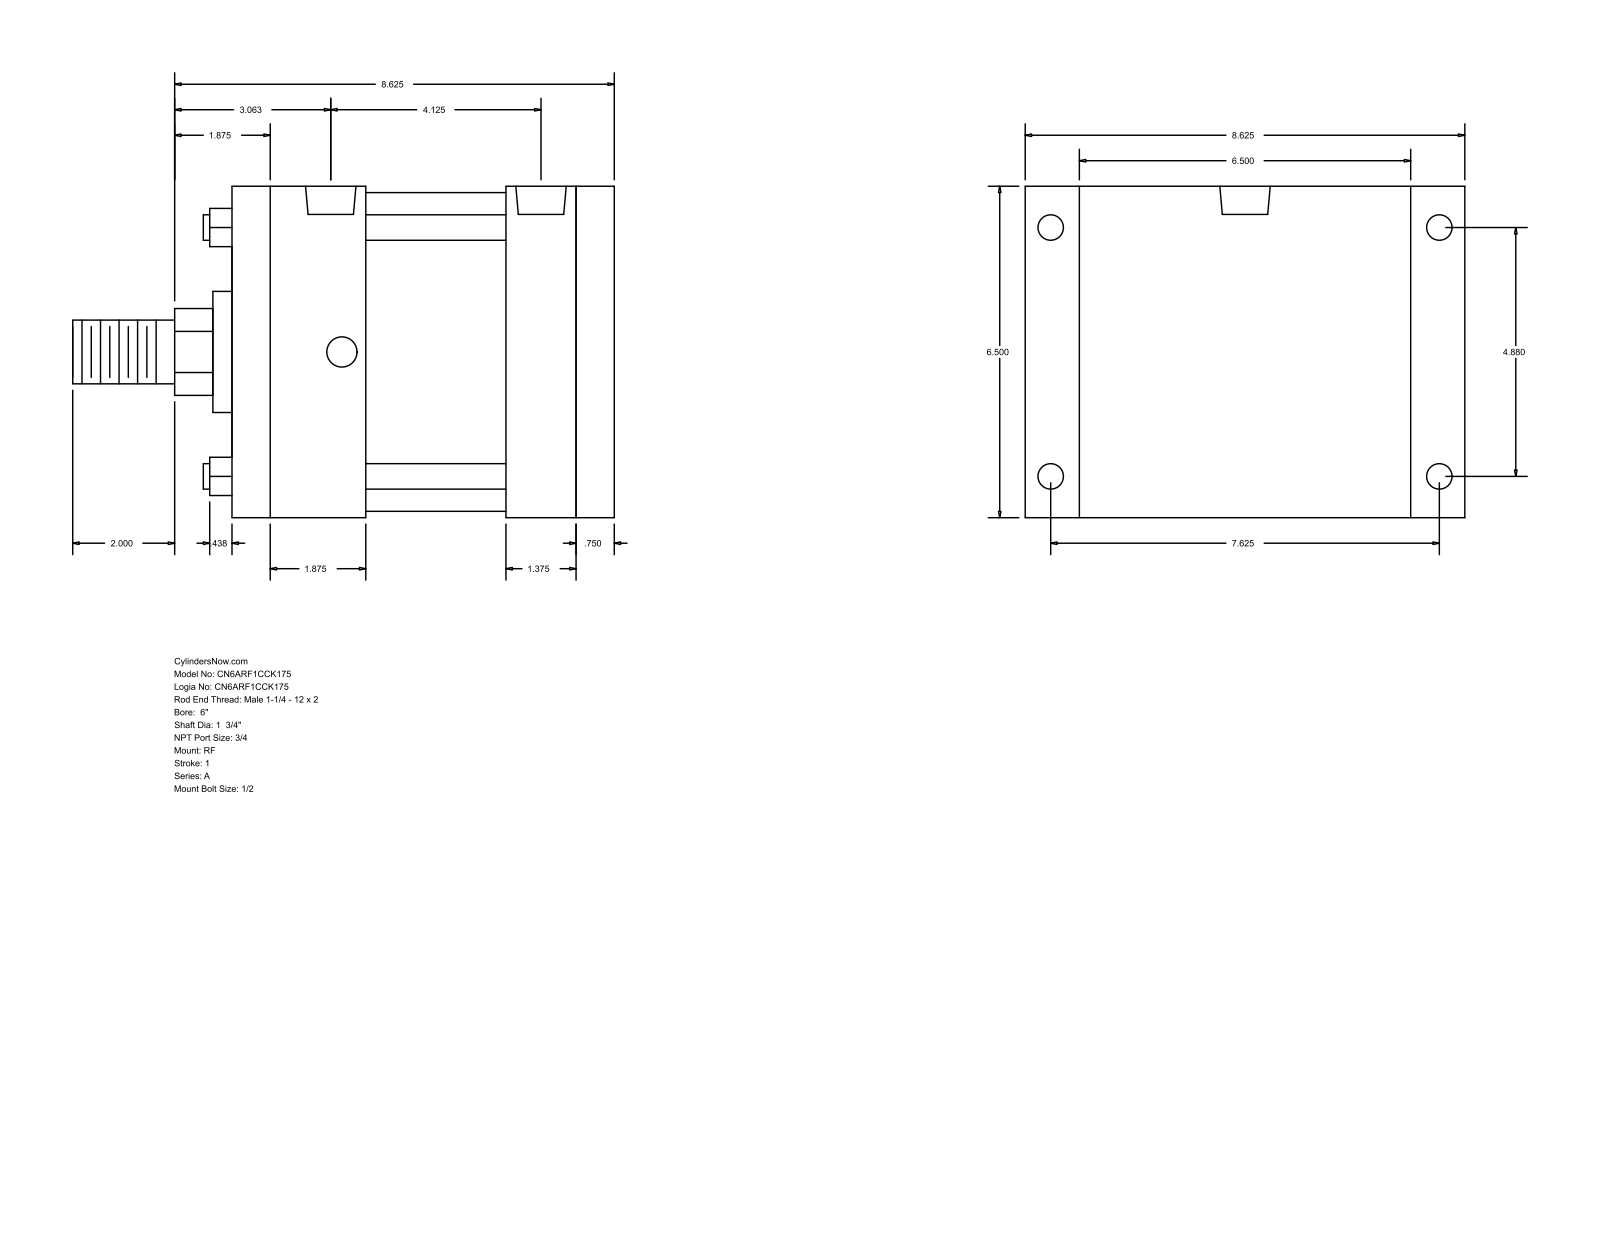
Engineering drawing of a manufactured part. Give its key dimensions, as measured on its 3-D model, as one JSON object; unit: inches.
{"part_name": "A_RF__0600_1.75", "step_written_by": "GSSL Pune (CONFIG_CONTROL_DESIGN)", "units": "inches", "bodies": {"solids": 0, "faces": 92, "planar": 64, "cylindrical": 28, "other": 0}, "overall_size": [10.625, 8.625, 6.5], "round_holes": [[0.5, 4], [0.594, 4], [0.989, 2]], "round_bosses_or_shafts": [[0.5, 4], [6.25, 1], [2.375, 1], [1.75, 1], [1.25, 1]], "partial_cylinders_radius": [[0.852, 1]], "face_to_face_distances": [6.5, 7.5, 6.75, 0.75, 2.75, 2.625, 4.125, 4.875, 5.375, 1.375], "hole_center_spacings": [0.219, 3.687, 3.906, 4.88, 7.625, 9.053, 4.125]}
